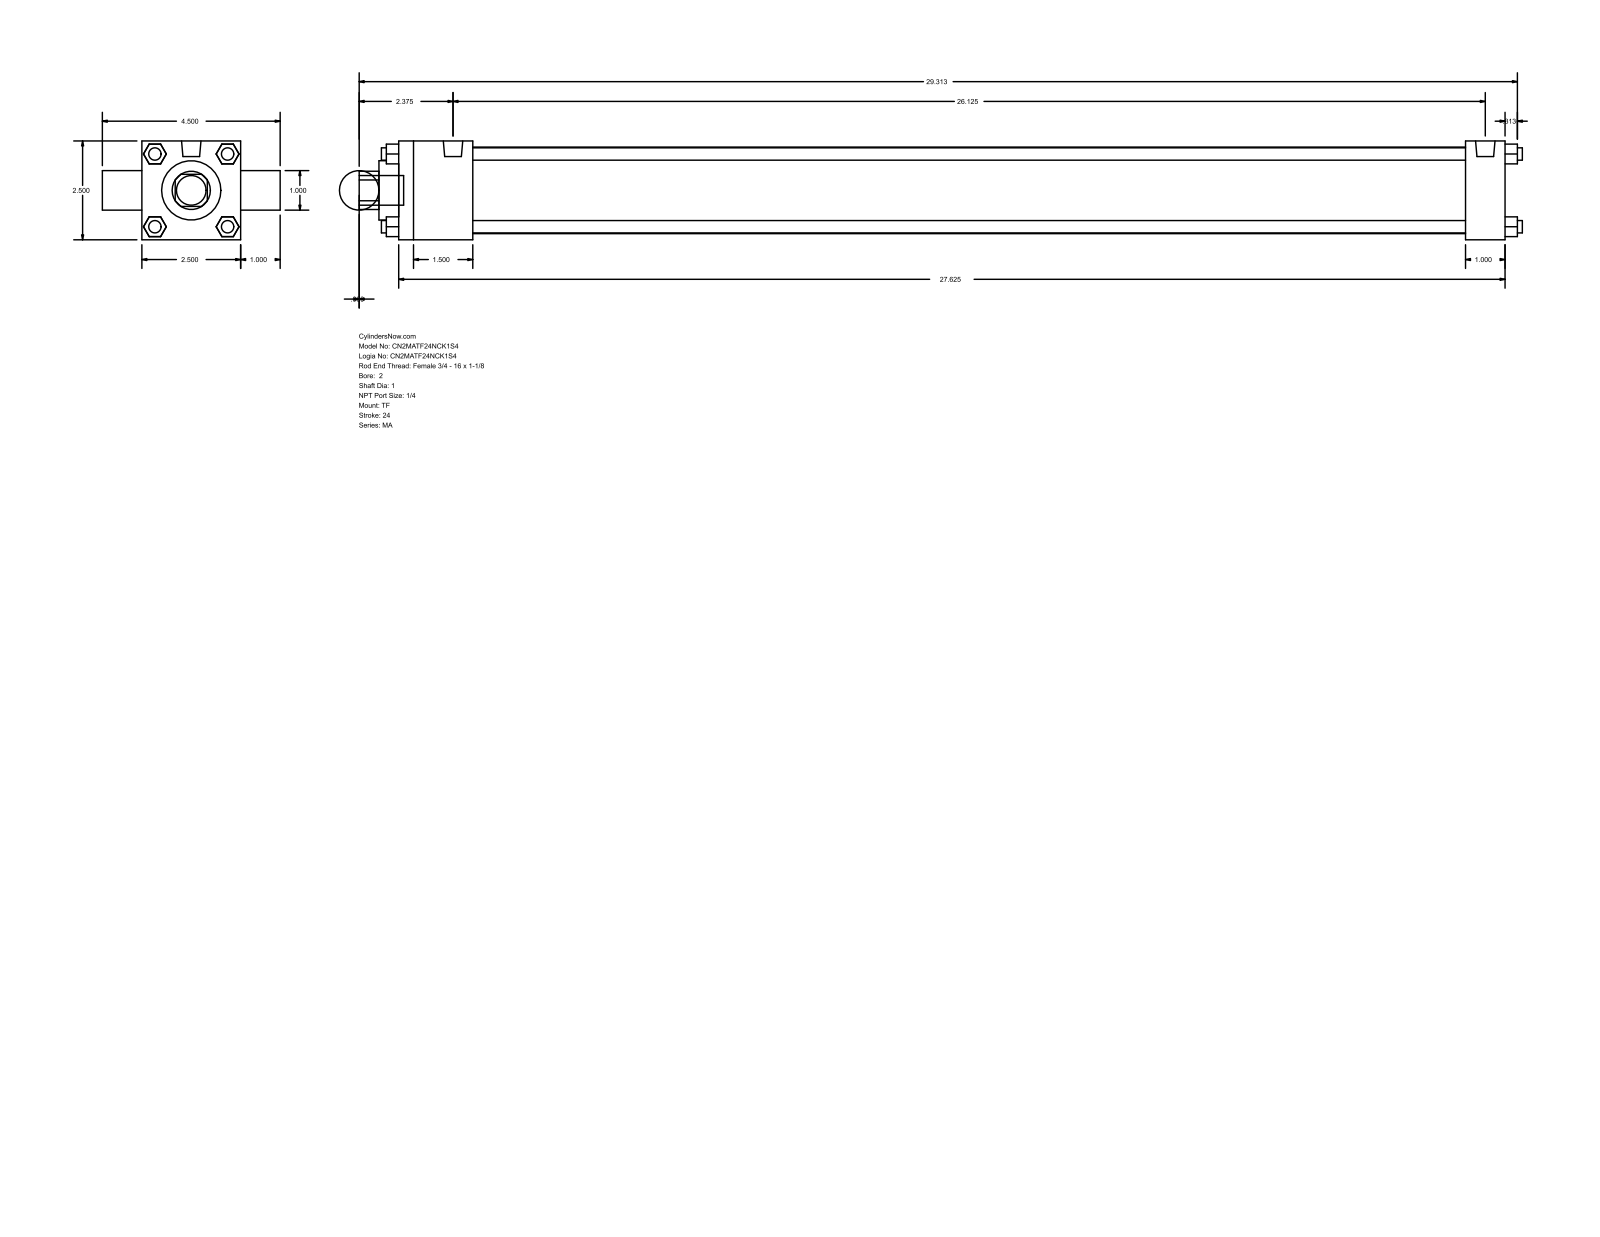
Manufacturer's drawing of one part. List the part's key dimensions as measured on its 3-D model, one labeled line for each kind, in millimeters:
Part name (STEP PRODUCT): MA_TF__0200_1
STEP written by: GSSL Pune (CONFIG_CONTROL_DESIGN)
Units: millimetres
Bodies: 0 solids, 120 faces (92 planar, 28 cylindrical, 0 other)
Overall size (bounding box): 747.71 × 114.3 × 63.5
Round holes (diameter × count): ⌀25.4 ×2, ⌀38.1 ×1, ⌀55.63 ×1
Round bosses / shafts (diameter × count): ⌀7.94 ×7, ⌀12.49 ×2, ⌀19.05 ×1
Partial cylindrical surfaces — rounded edges, fillets, slot ends (radius × count): R12.29 ×1
Main face-to-face distances: 63.5, 25.4, 711.2, 12.7, 47.63, 685.8, 638.17, 663.57, 88.9, 23.37
